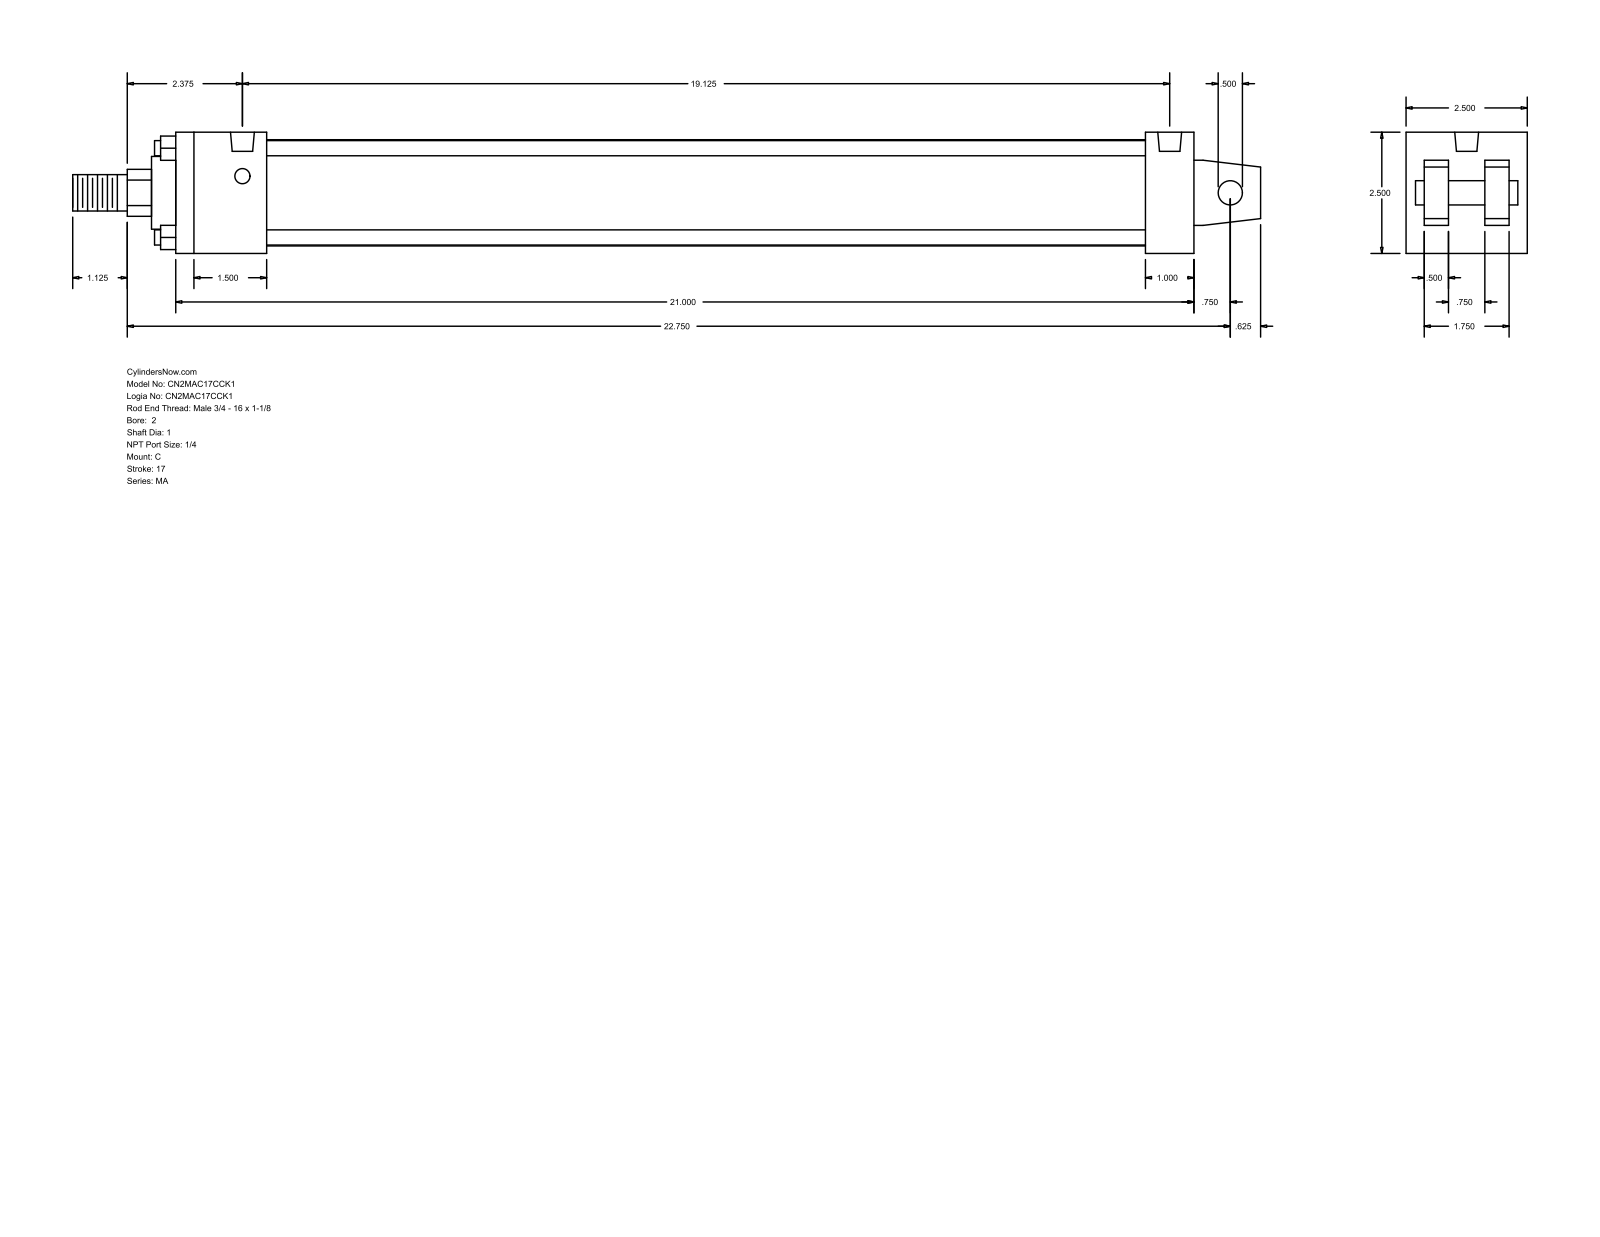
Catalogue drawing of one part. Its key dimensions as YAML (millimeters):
part_name: "MA_C__0200_1"
step_written_by: "GSSL Pune (CONFIG_CONTROL_DESIGN)"
units: millimeters
bodies: {solids: 0, faces: 103, planar: 76, cylindrical: 27, other: 0}
overall_size: [622.3, 63.5, 63.5]
round_holes:
  - {diameter: 7.94, count: 4}
  - {diameter: 12.49, count: 2}
round_bosses_or_shafts:
  - {diameter: 7.94, count: 4}
  - {diameter: 55.63, count: 1}
  - {diameter: 38.1, count: 1}
  - {diameter: 25.4, count: 1}
  - {diameter: 19.05, count: 1}
  - {diameter: 12.7, count: 1}
partial_cylinders:
  - {radius: 12.29, count: 1}
face_to_face_distances: [63.5, 12.7, 533.4, 22.22, 41.28, 9.52, 53.98, 31.76, 47.63, 25.4]
hole_center_spacings: [485.77]
